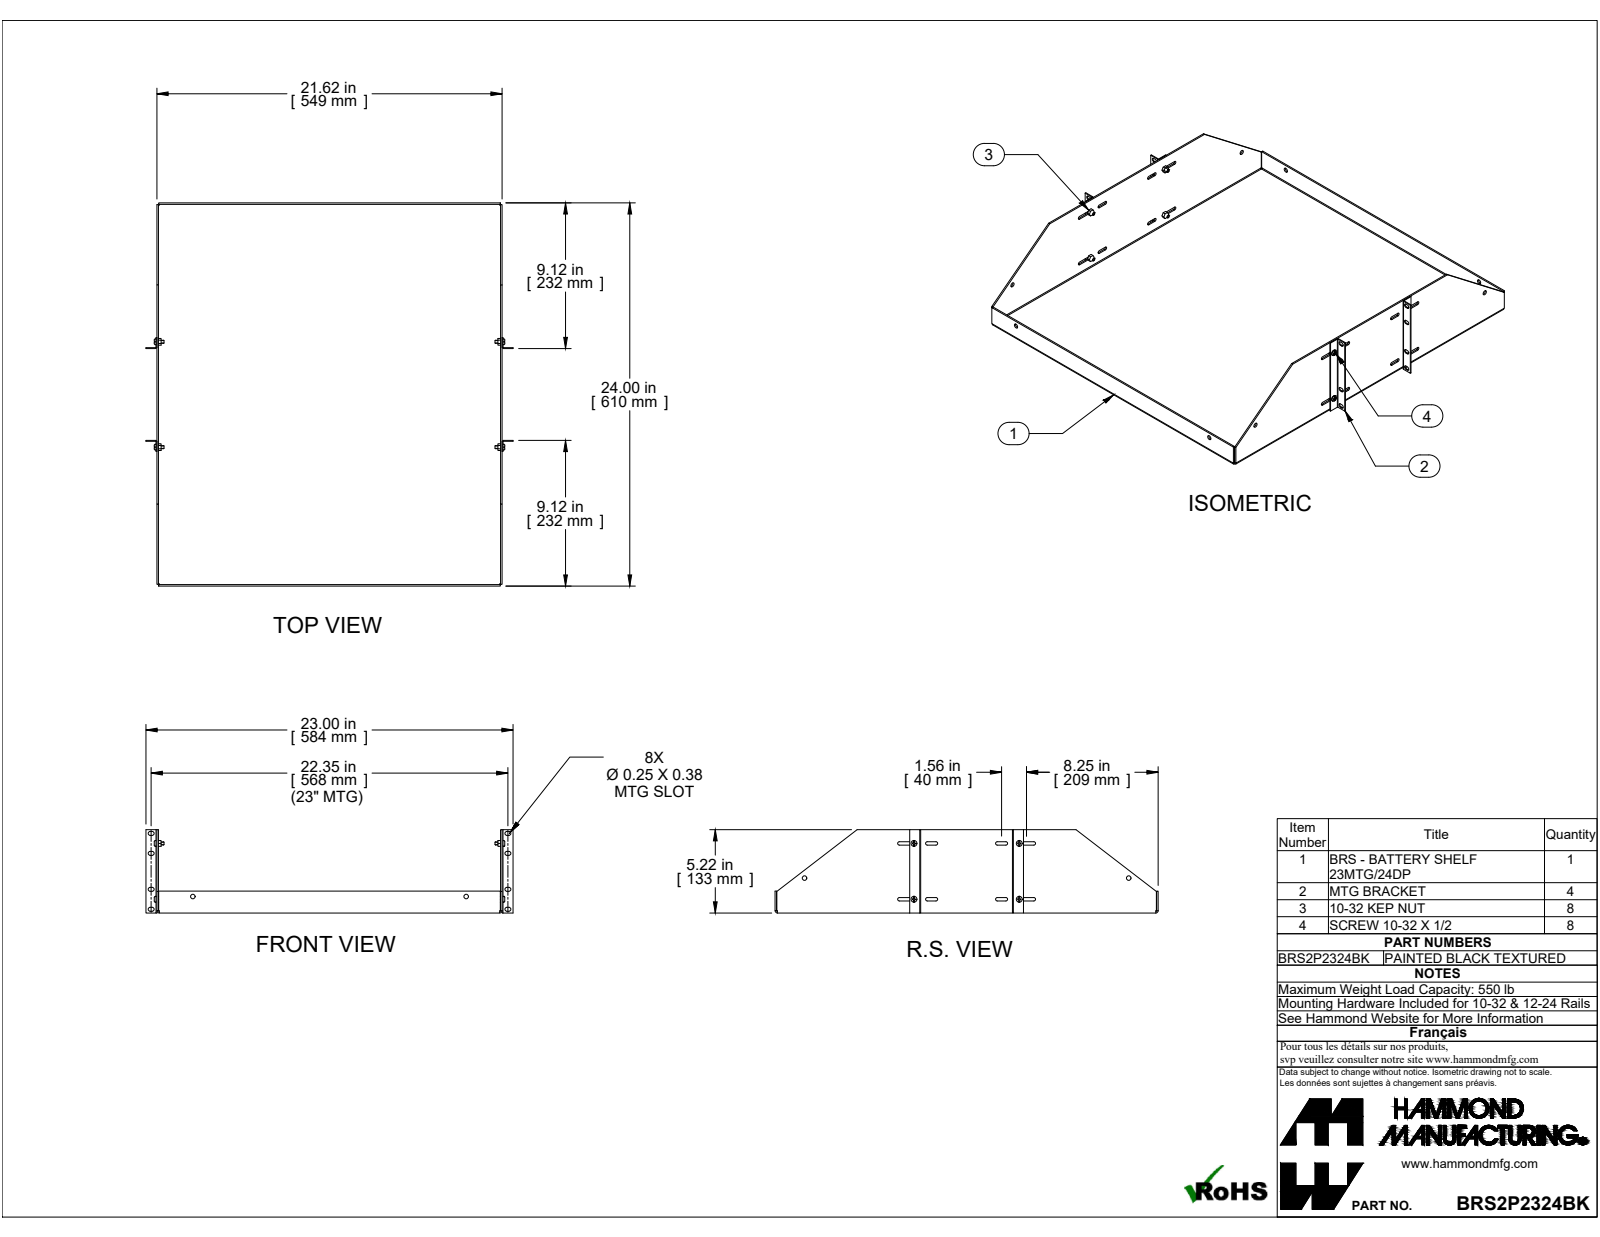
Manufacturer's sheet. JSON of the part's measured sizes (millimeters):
{"part_name": "BRS2P2324BK", "step_written_by": "SolidWorks 2019 (CONFIG_CONTROL_DESIGN)", "units": "millimeters", "bodies": {"solids": 21, "faces": 466, "planar": 322, "cylindrical": 120, "other": 24}, "overall_size": [609.6, 584.2, 132.5], "volume_mm3": 1229000, "surface_area_mm2": 1045000, "round_holes": [[4, 4], [5.4, 4], [7.1, 4]], "round_bosses_or_shafts": [[9.4, 4], [4.8, 4]], "partial_cylinders_radius": [[3.2, 16], [2.7, 12], [0.7, 4], [1.2, 4], [2.2, 4], [3.6, 4]], "face_to_face_distances": [2.4, 546.9, 2.4, 549.3, 544.4, 607.2, 609.6, 604.8, 1.4, 3.9], "hole_center_spacings": [88.9, 167.6, 177.4, 182.7, 189.7, 343.4, 346.2, 435]}
